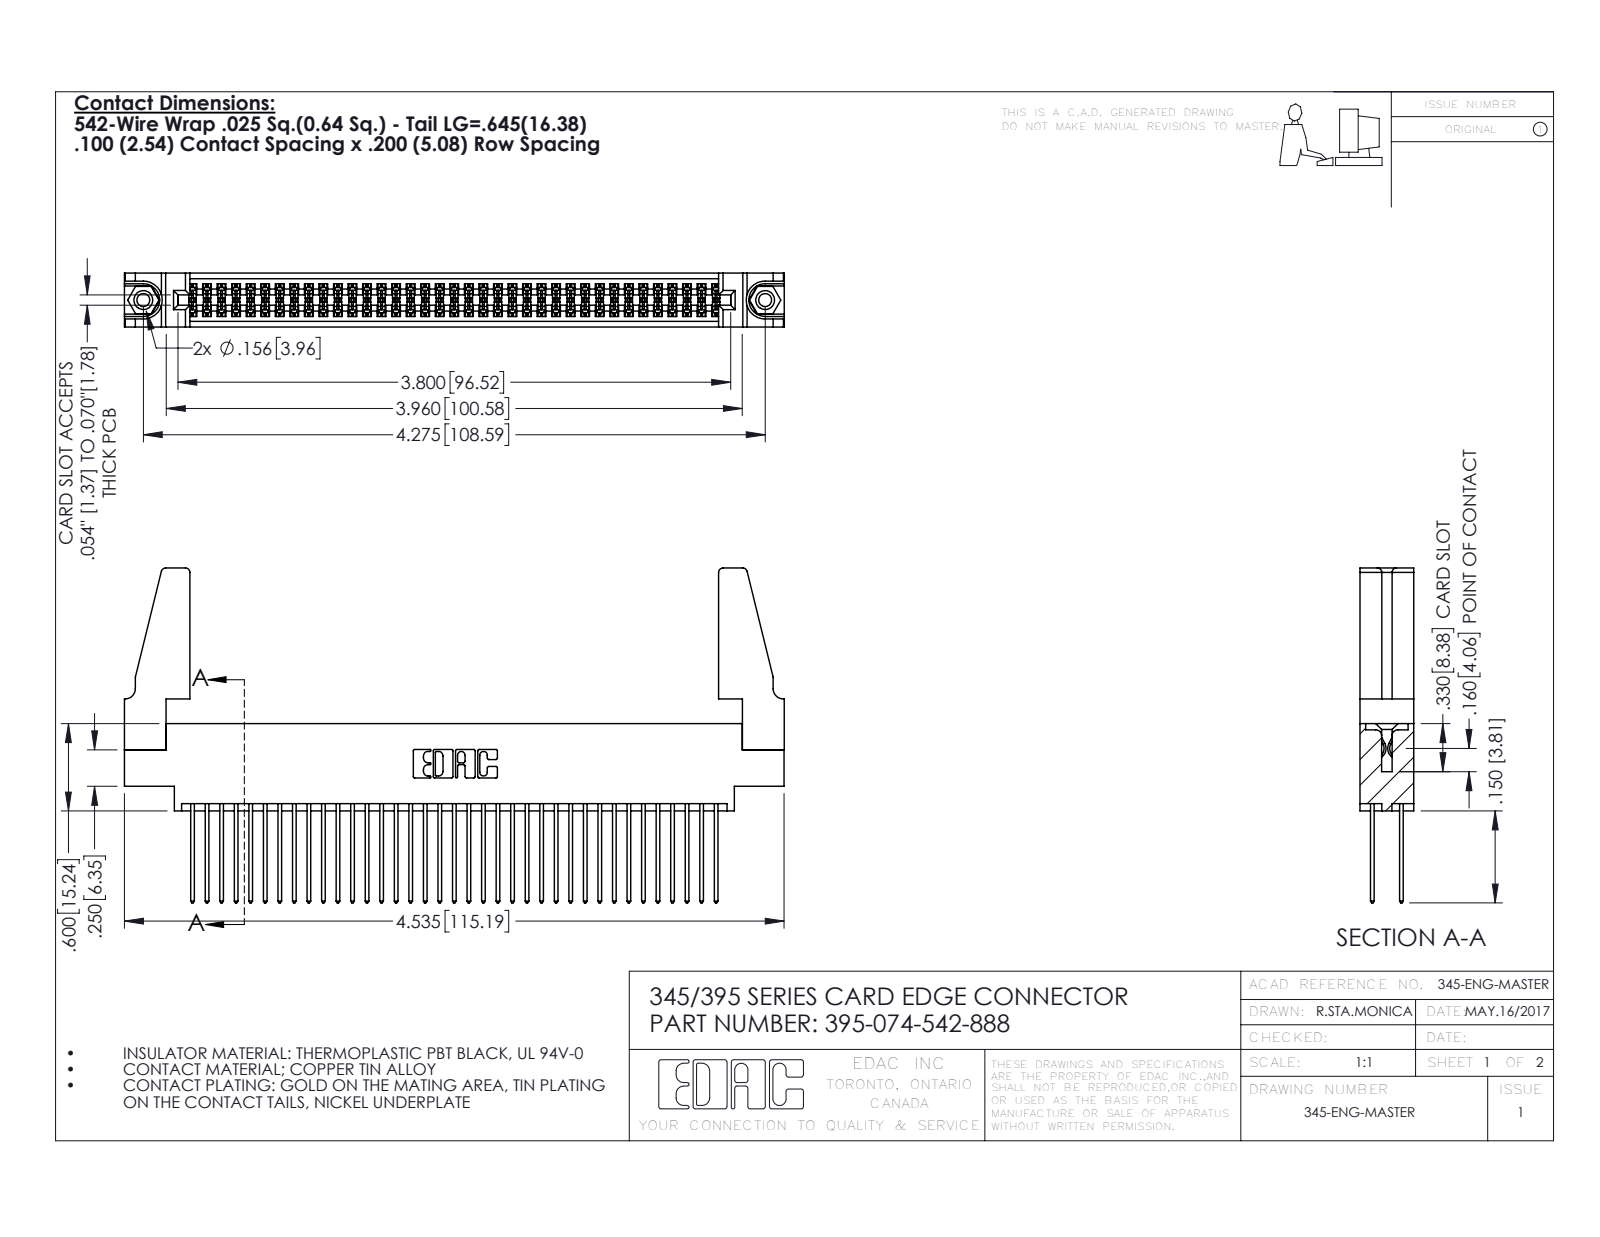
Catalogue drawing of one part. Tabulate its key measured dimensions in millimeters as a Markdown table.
| quantity | value |
| --- | --- |
| part name | 345 Part_0.170 Offset - 0.156 Dia-TH; 345-220-078_345-220-088; 345-292-001_345-293-142; 345-250-001_345-250-001-102 (+1 more) |
| STEP written by | SolidWorks 2016 (CONFIG_CONTROL_DESIGN) |
| units | millimeters |
| bodies | 79 solids, 3954 faces (2598 planar, 1340 cylindrical, 16 other) |
| overall size | 115.2 × 58.5 × 9.4 |
| volume | 14 600 mm³ |
| surface area | 21 600 mm² |
| round holes (diameter × count) | 2.3 × 2, 3.2 × 2, 4 × 2, 1.6 × 1 |
| round bosses / shafts (diameter × count) | 3.9 × 2 |
| partial cylindrical surfaces (radius × count) | 0.2 × 111, 0.3 × 74, 0.3 × 22, 0.8 × 8, 0.2 × 6, 0.8 × 6, 0.7 × 3, 0.4 × 2 |
| main face-to-face distances | 1.8, 7.6, 9.4, 2.5, 6.9, 0.6, 5.1, 5.7, 4.4, 3.8 |
| hole center spacings | 6.9, 102.6, 108.6 |
